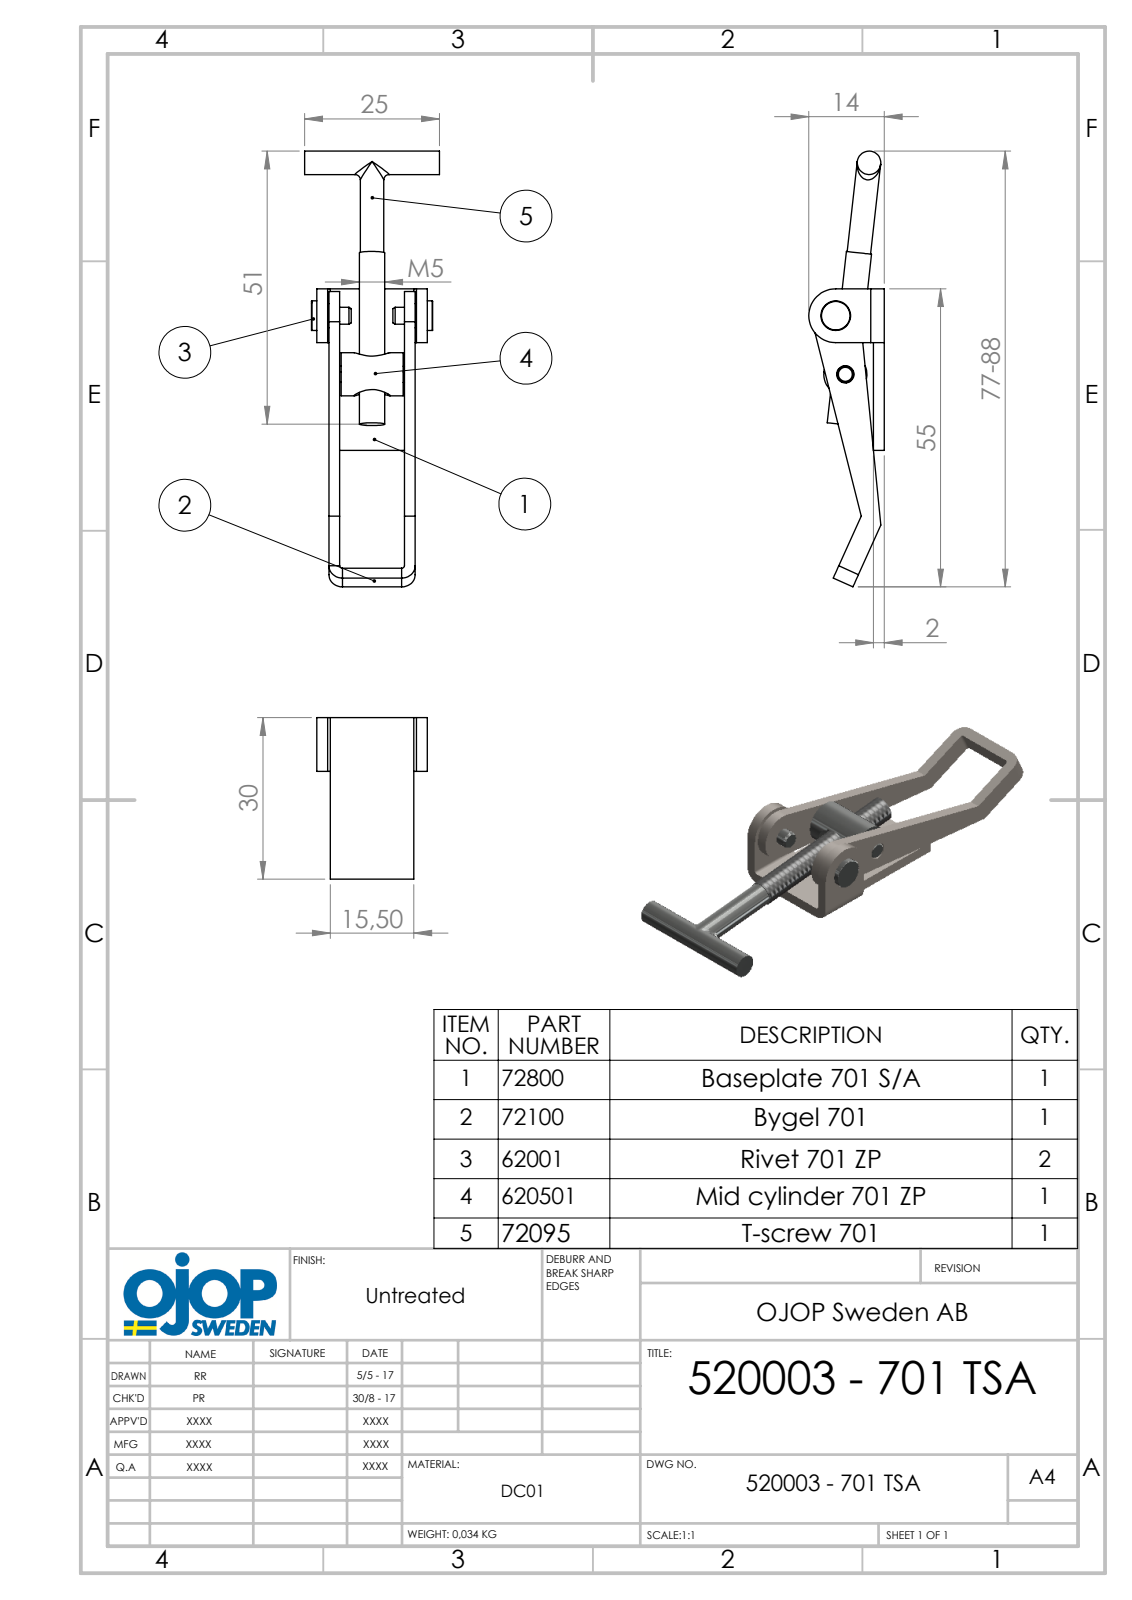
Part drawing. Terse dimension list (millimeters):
name: 701 - SA; 701 - Bygel; 701 - Ansatsnit; 701 - Mid Cylinder (+2 more)
written by: SolidWorks 2015 (AUTOMOTIVE_DESIGN)
unit: mm
bodies: 6 solids, 121 faces (51 planar, 52 cylindrical, 18 other)
size: 78.6 × 25 × 14
volume: 4 448 mm³; area: 5 385 mm²
holes: 2× ⌀3.2, 1× ⌀4.5, 1× ⌀4.8
bosses: 2× ⌀4.36, 1× ⌀8, 1× ⌀5.5, 1× ⌀4.7, 1× ⌀3.15, 1× ⌀3
rounds: 4× R0.5, 4× R2.5, 1× R4.5, 1× R5
face distances: 2, 14, 2.25, 16, 16.25, 12, 4.25, 18.25, 18.5, 14.25
hole spacings: 11.02
